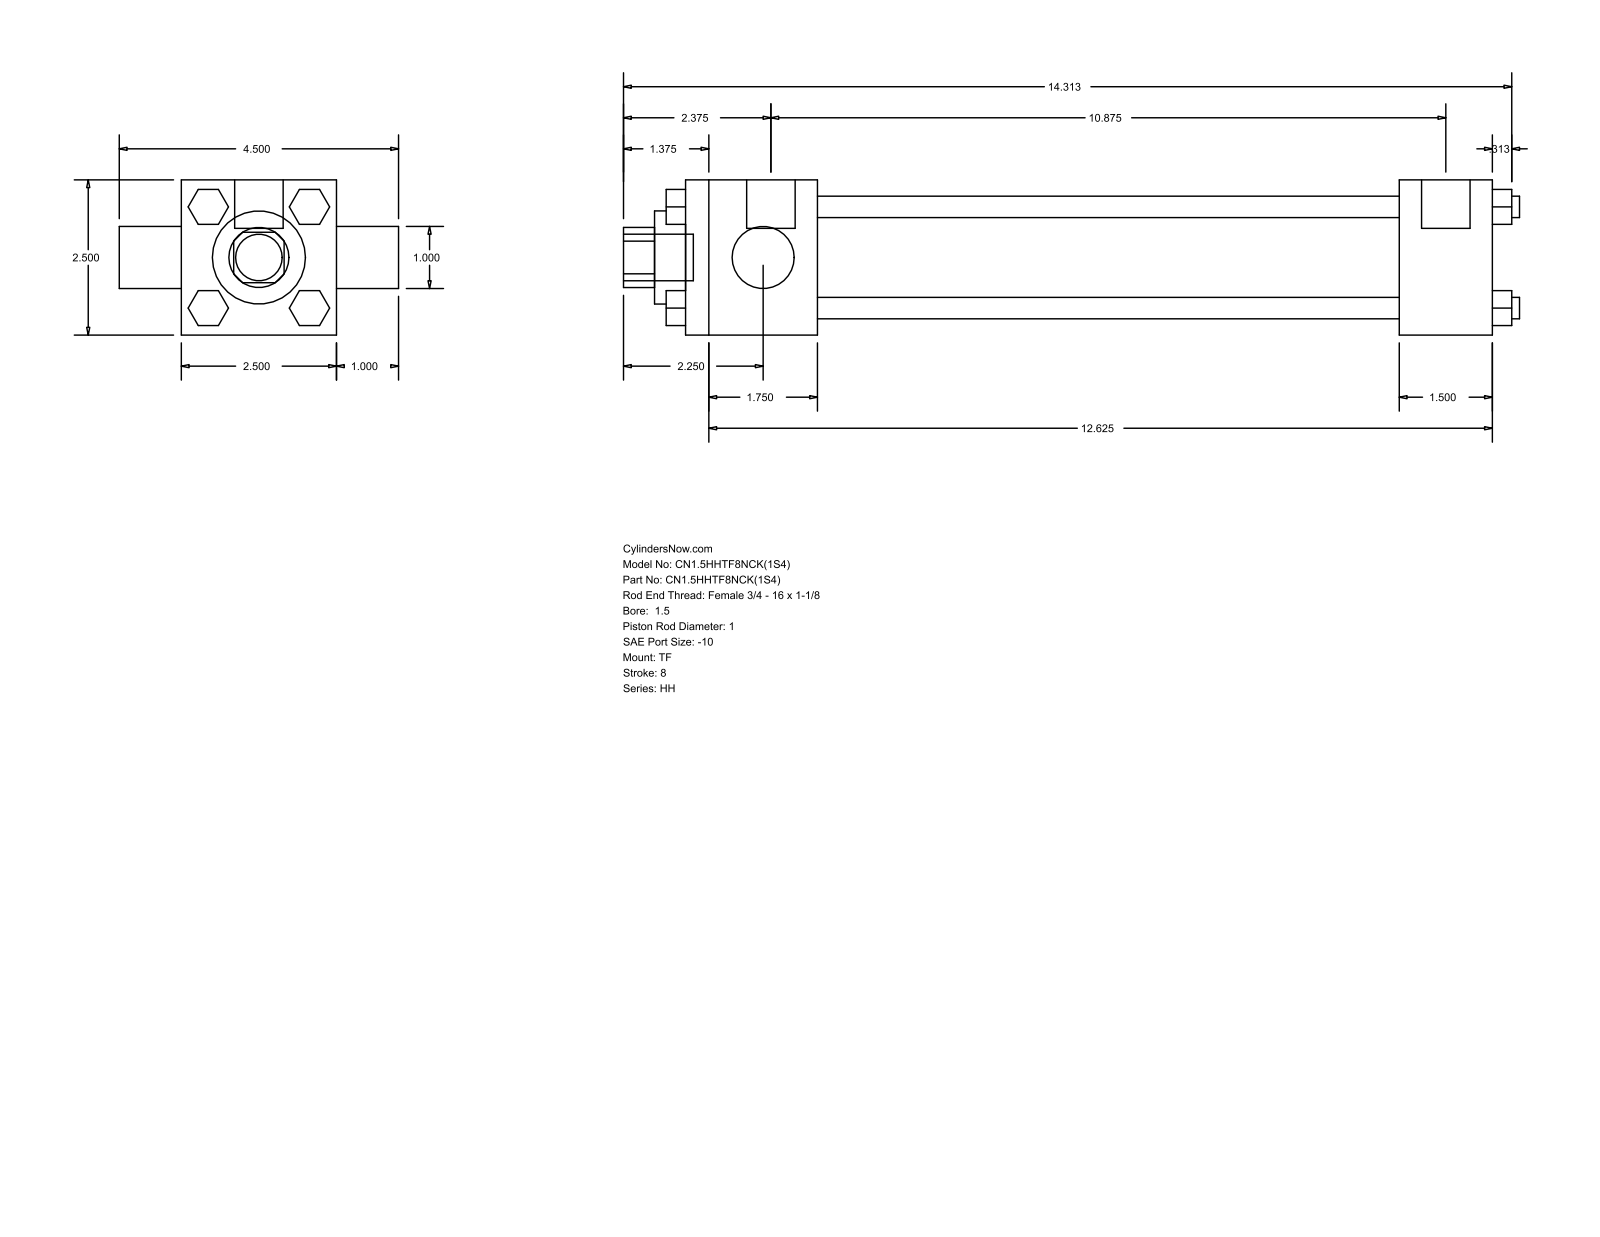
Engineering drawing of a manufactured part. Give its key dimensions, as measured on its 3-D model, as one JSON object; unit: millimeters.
{"part_name": "HH_TF__0150_1", "step_written_by": "GSSL Pune (CONFIG_CONTROL_DESIGN)", "units": "millimeters", "bodies": {"solids": 0, "faces": 120, "planar": 92, "cylindrical": 28, "other": 0}, "overall_size": [366.71, 114.3, 63.5], "round_holes": [[25.4, 2], [38.1, 1], [44.45, 1]], "round_bosses_or_shafts": [[8.76, 4], [5.56, 3], [19.84, 2], [19.05, 1]], "partial_cylinders_radius": [[12.29, 1]], "face_to_face_distances": [63.5, 276.22, 238.12, 38.1, 53.98, 292.1, 330.2, 338.14, 25.4, 20.7]}
